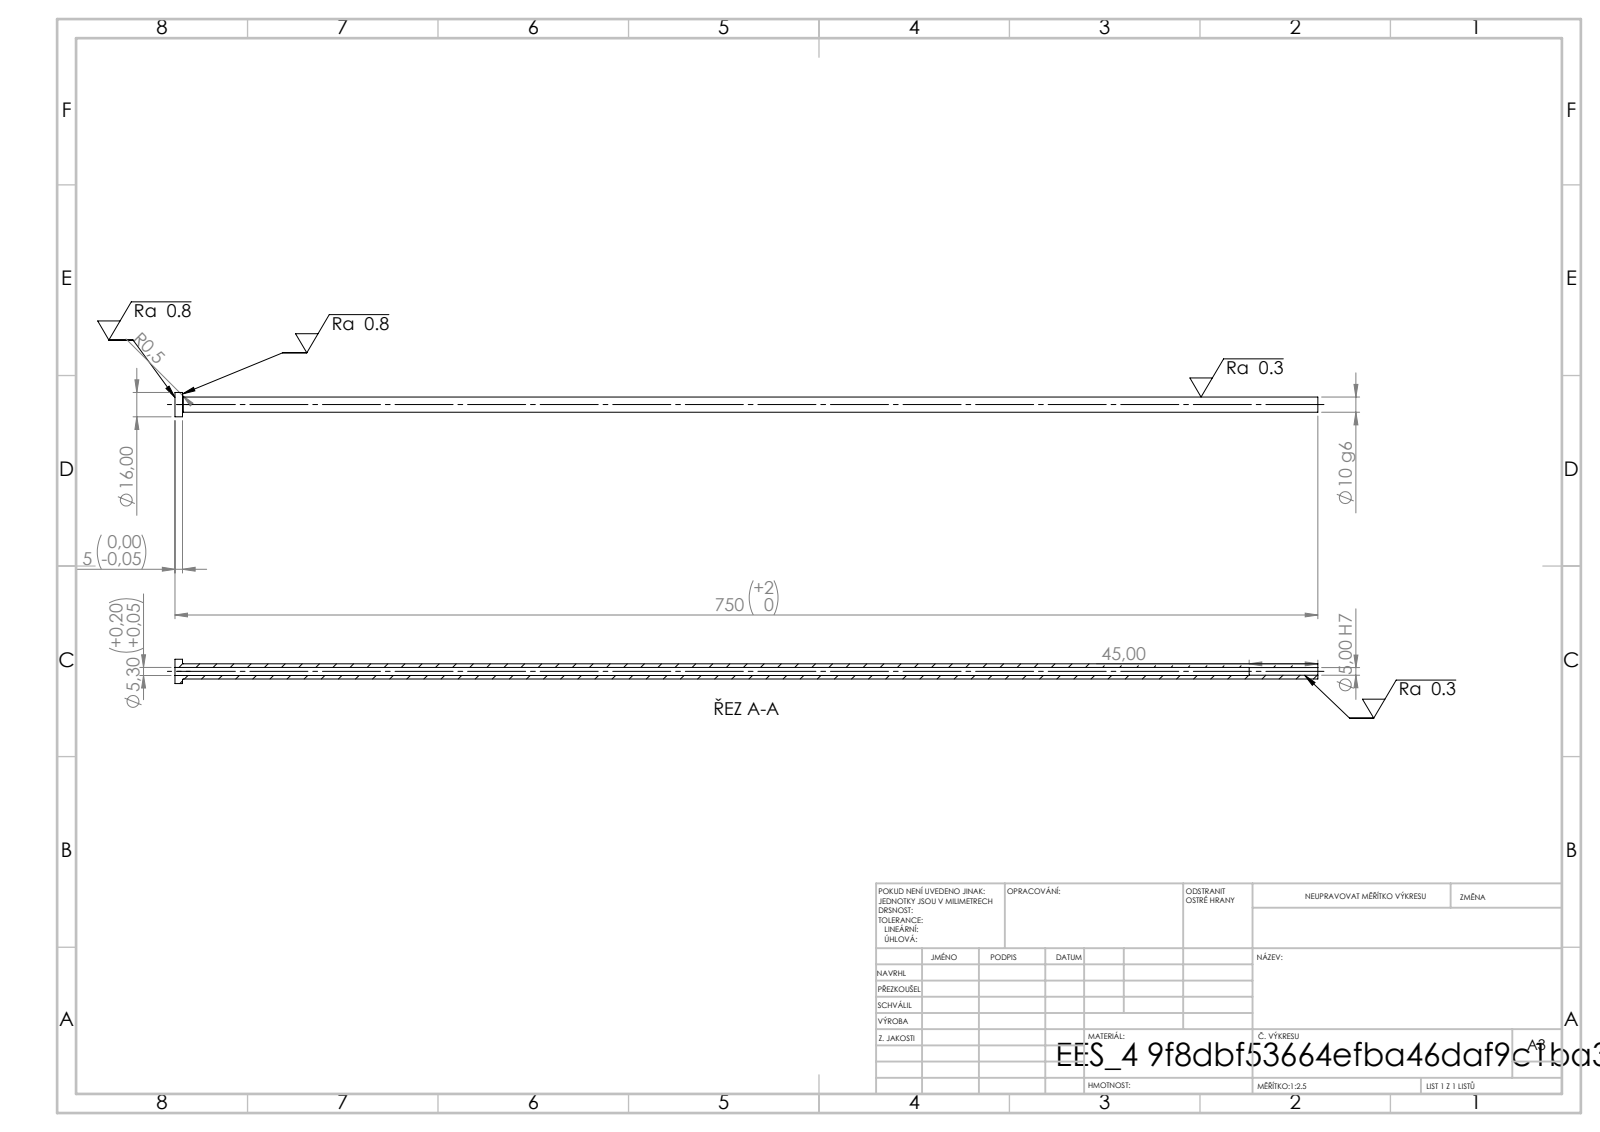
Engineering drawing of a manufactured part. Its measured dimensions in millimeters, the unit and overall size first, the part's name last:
Units: millimetres
Overall size (bounding box): 750 × 16 × 16
Round holes (diameter × count): ⌀5 ×1, ⌀5.3 ×1
Round bosses / shafts (diameter × count): ⌀16 ×1, ⌀10 ×1
Main face-to-face distances: 5, 750, 745, 705, 700, 45
Volume: 43 082 mm³ · Surface area: 36 458 mm²
Bodies: 1 solid, 14 faces (4 planar, 8 cylindrical, 2 other)
STEP written by: SolidWorks 2019 (CONFIG_CONTROL_DESIGN)
